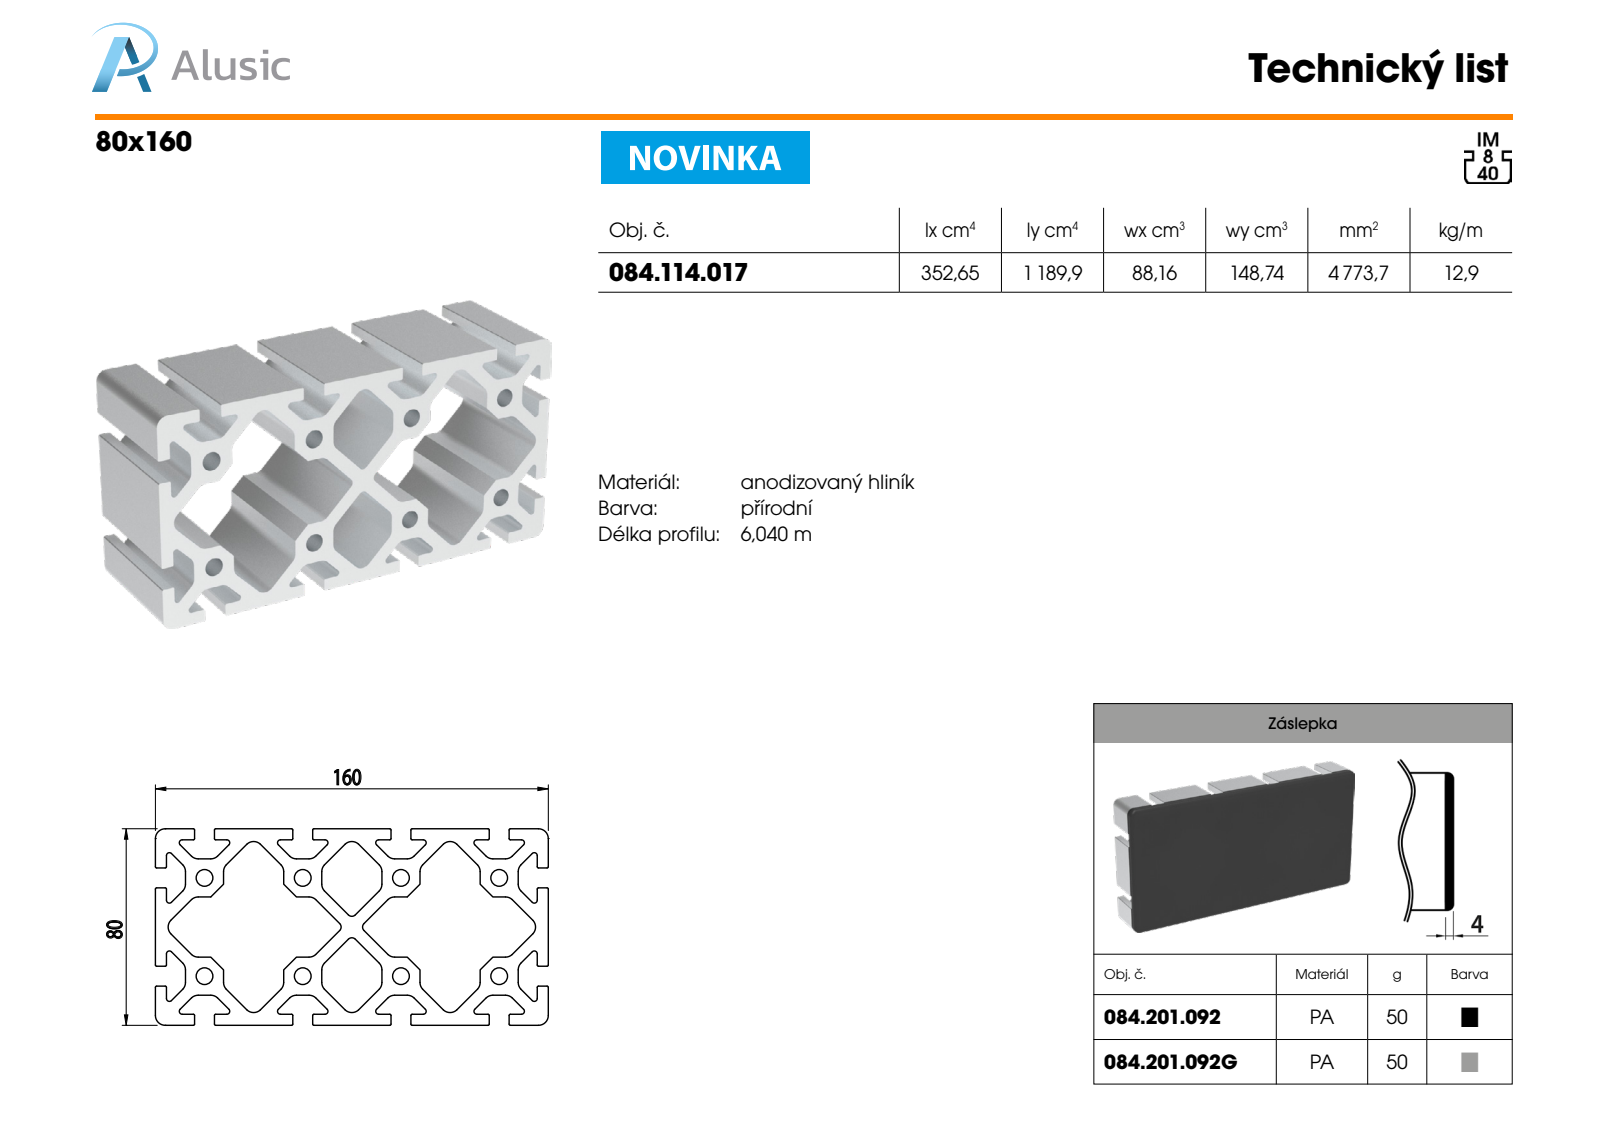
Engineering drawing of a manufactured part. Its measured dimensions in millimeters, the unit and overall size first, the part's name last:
Units: millimetres
Overall size (bounding box): 160 × 100 × 80
Round holes (diameter × count): ⌀6.8 ×8
Partial cylindrical surfaces — rounded edges, fillets, slot ends (radius × count): R4 ×60, R0.5 ×48, R1.2 ×24, R2 ×4
Main face-to-face distances: 28.28, 56.56, 5, 80, 40, 51.56, 23.28, 4.5, 33.28, 84.84
Hole centre spacings: 40, 56.57, 80, 89.44, 120, 126.49
Volume: 477 371 mm³ · Surface area: 181 438 mm²
Bodies: 1 solid, 314 faces (154 planar, 160 cylindrical, 0 other)
Part name (STEP PRODUCT): 084.114.017
STEP written by: SolidWorks 2018 (AUTOMOTIVE_DESIGN)
